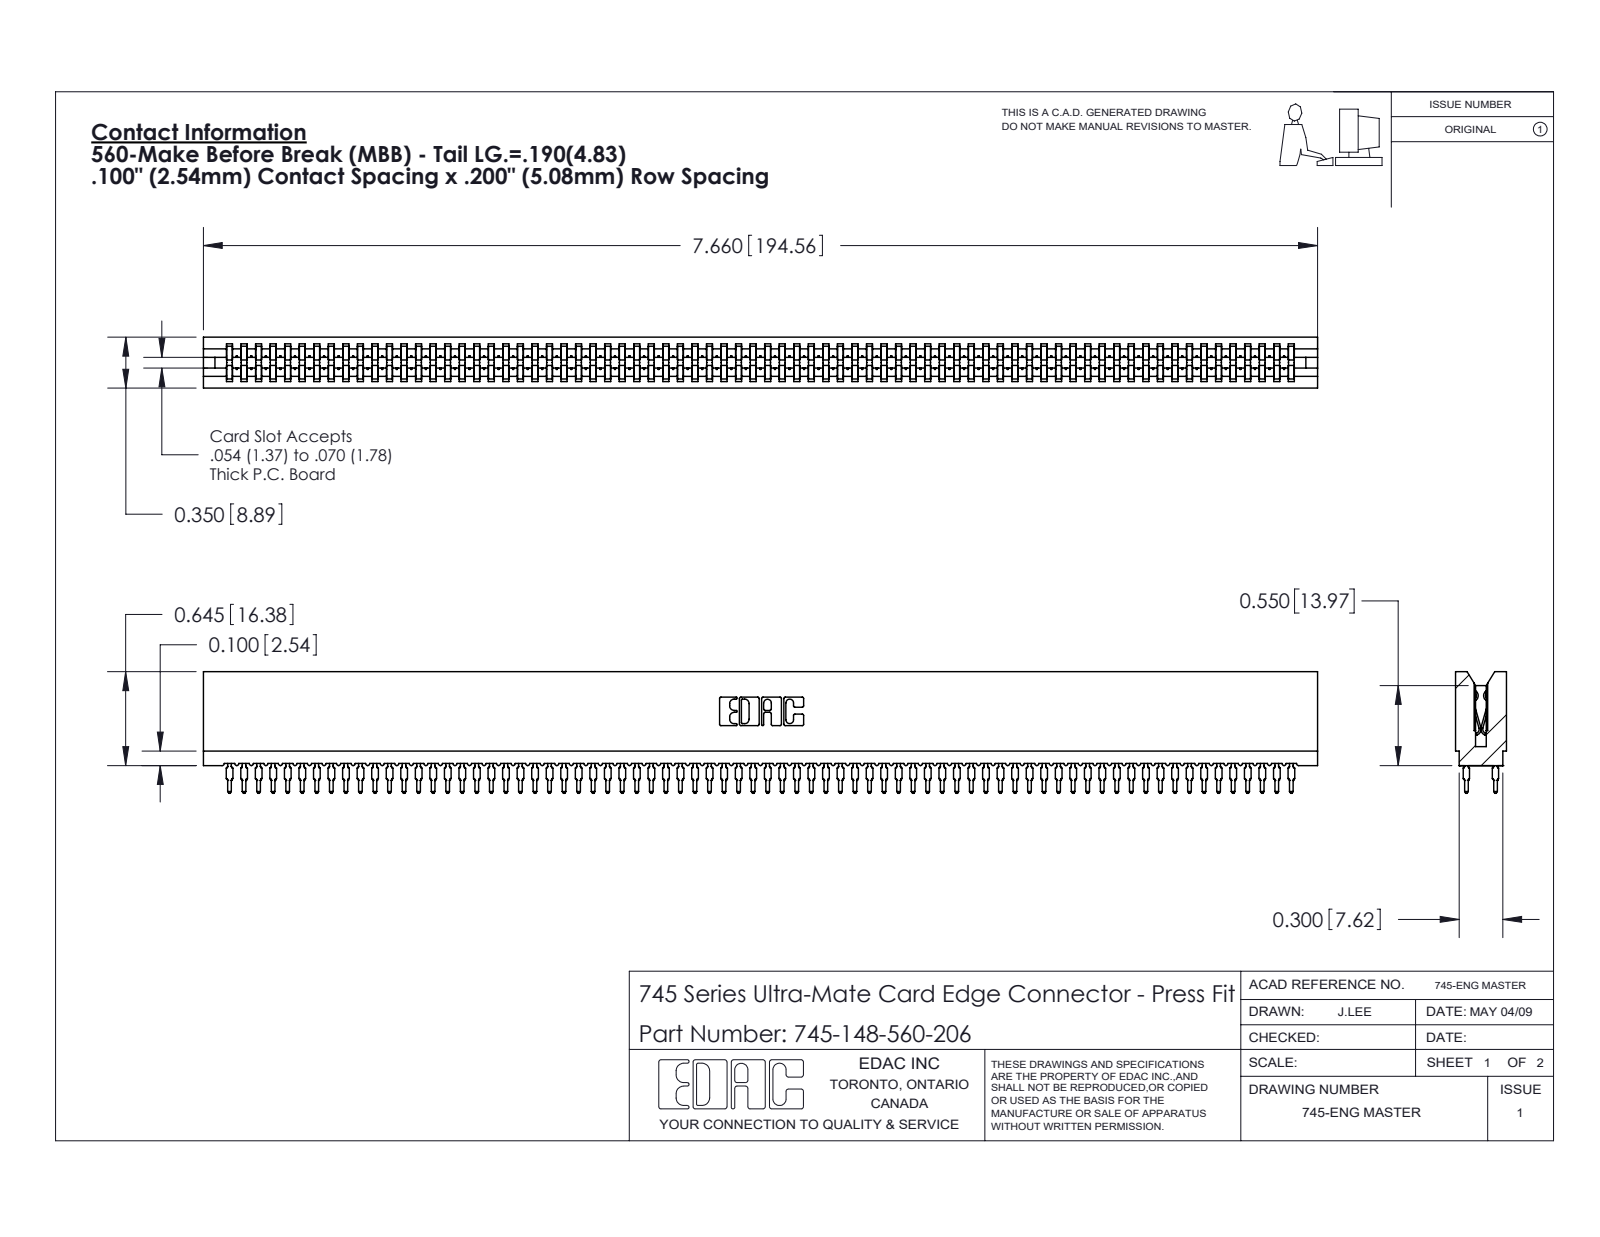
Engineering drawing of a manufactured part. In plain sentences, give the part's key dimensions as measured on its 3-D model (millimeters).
The part is named "745-292-001_560; 745 Part_Insulator Option - 06; 745-148-560-206". Its 3-D file was written by "SolidWorks 2020 (CONFIG_CONTROL_DESIGN)". It is 149 solids with 14674 faces: 7604 planar, 3222 cylindrical and 3848 other. Overall it measures 194.6 by 21.2 by 8.9 millimeters. Its volume is 17 850 cubic millimeters and its surface area 39 400 square millimeters. Partial cylindrical surfaces (rounded edges, fillets, slot ends): 296 of radius 0.5, 148 of radius 0.4, 22 of radius 0.3, 8 of radius 0.1, 8 of radius 0.3, 6 of radius 0.2, 6 of radius 0.8, 3 of radius 0.7. The main face-to-face distances are 8.9, 1.6, 7.3, 1.1, 7.7, 0.5, 6.2, 3.5, 5.4, 2.4.
